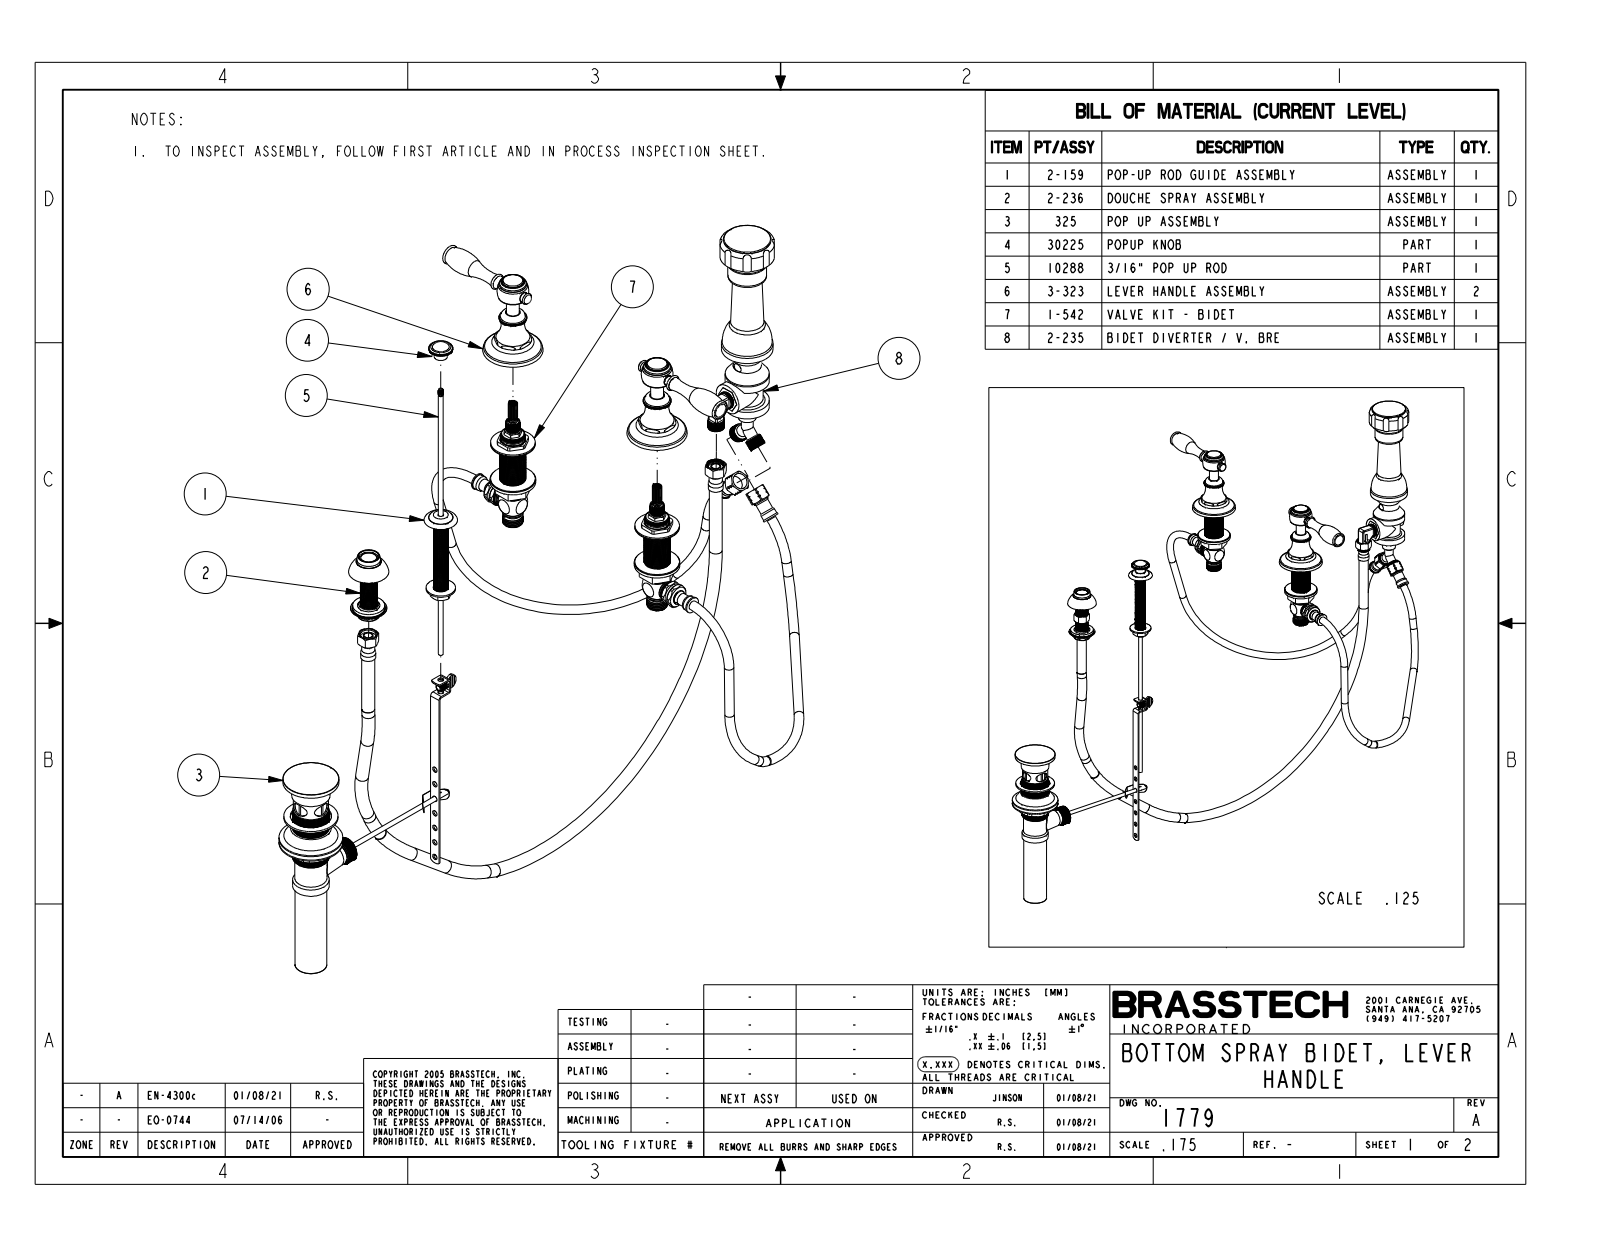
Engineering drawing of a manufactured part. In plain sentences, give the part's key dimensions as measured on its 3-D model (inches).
The part is named "1779". Its 3-D file was written by "CREO PARAMETRIC BY PTC INC, 2018400 (CONFIG_CONTROL_DESIGN)". It is 5 solids with 699 faces: 471 planar, 66 cylindrical and 162 other. Overall it measures 22.855 by 15.292 by 5.353 inches. Its volume is 21.79 cubic inches and its surface area 103.7 square inches. Round holes: 2 of diameter 0.855, 1 of diameter 0.41, 1 of diameter 0.625, 1 of diameter 0.792, 1 of diameter 0.94. Round bosses or shafts: 2 of diameter 0.84, 2 of diameter 0.5, 1 of diameter 2.025, 1 of diameter 1.52, 1 of diameter 0.925, 1 of diameter 0.775, 1 of diameter 0.392. Partial cylindrical surfaces (rounded edges, fillets, slot ends): 8 of radius 0.21, 1 of radius 0.357, 1 of radius 1.077. The main face-to-face distances are 2.54, 3.468, 0.928, 1.375, 0.674, 1.866, 2.794, 4, 3.25, 2.576. The hole center spacings are 12.649, 8.
